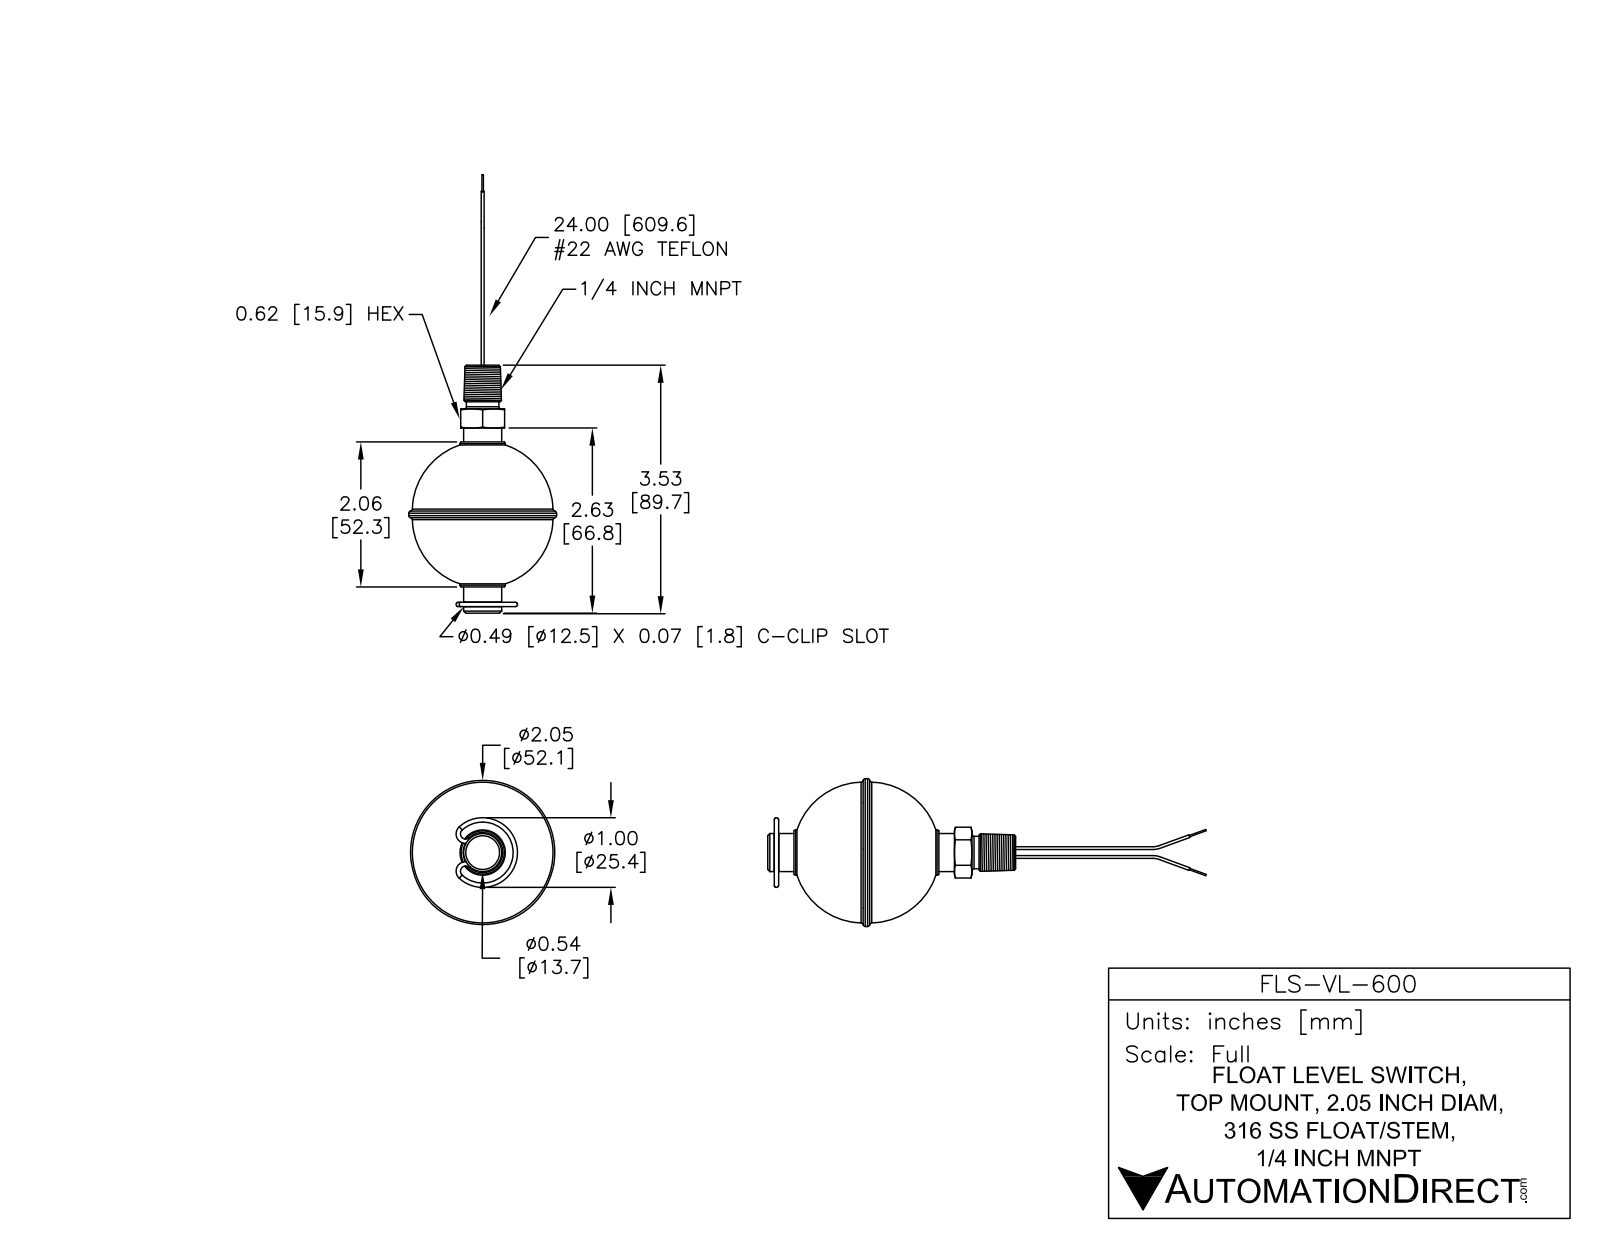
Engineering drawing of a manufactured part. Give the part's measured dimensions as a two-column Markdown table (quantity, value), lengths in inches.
| quantity | value |
| --- | --- |
| part name | FLS-VL-600 |
| STEP written by | SolidWorks 2013 (AUTOMOTIVE_DESIGN) |
| units | inches |
| bodies | 6 solids, 98 faces (26 planar, 30 cylindrical, 42 other) |
| overall size | 6.229 × 2.125 × 2.125 |
| volume | 4.768 in³ |
| surface area | 30.12 in² |
| round holes (diameter × count) | 0.46 × 1, 0.56 × 1 |
| round bosses / shafts (diameter × count) | 0.04 × 4, 0.02 × 2, 2.125 × 1, 2.025 × 1, 2.025 × 1, 0.53 × 1, 0.45 × 1 |
| main face-to-face distances | 0.625, 2.76, 0.07, 2.69, 3.38, 3.31, 0.62, 0.12, 0.19, 2.88 |
